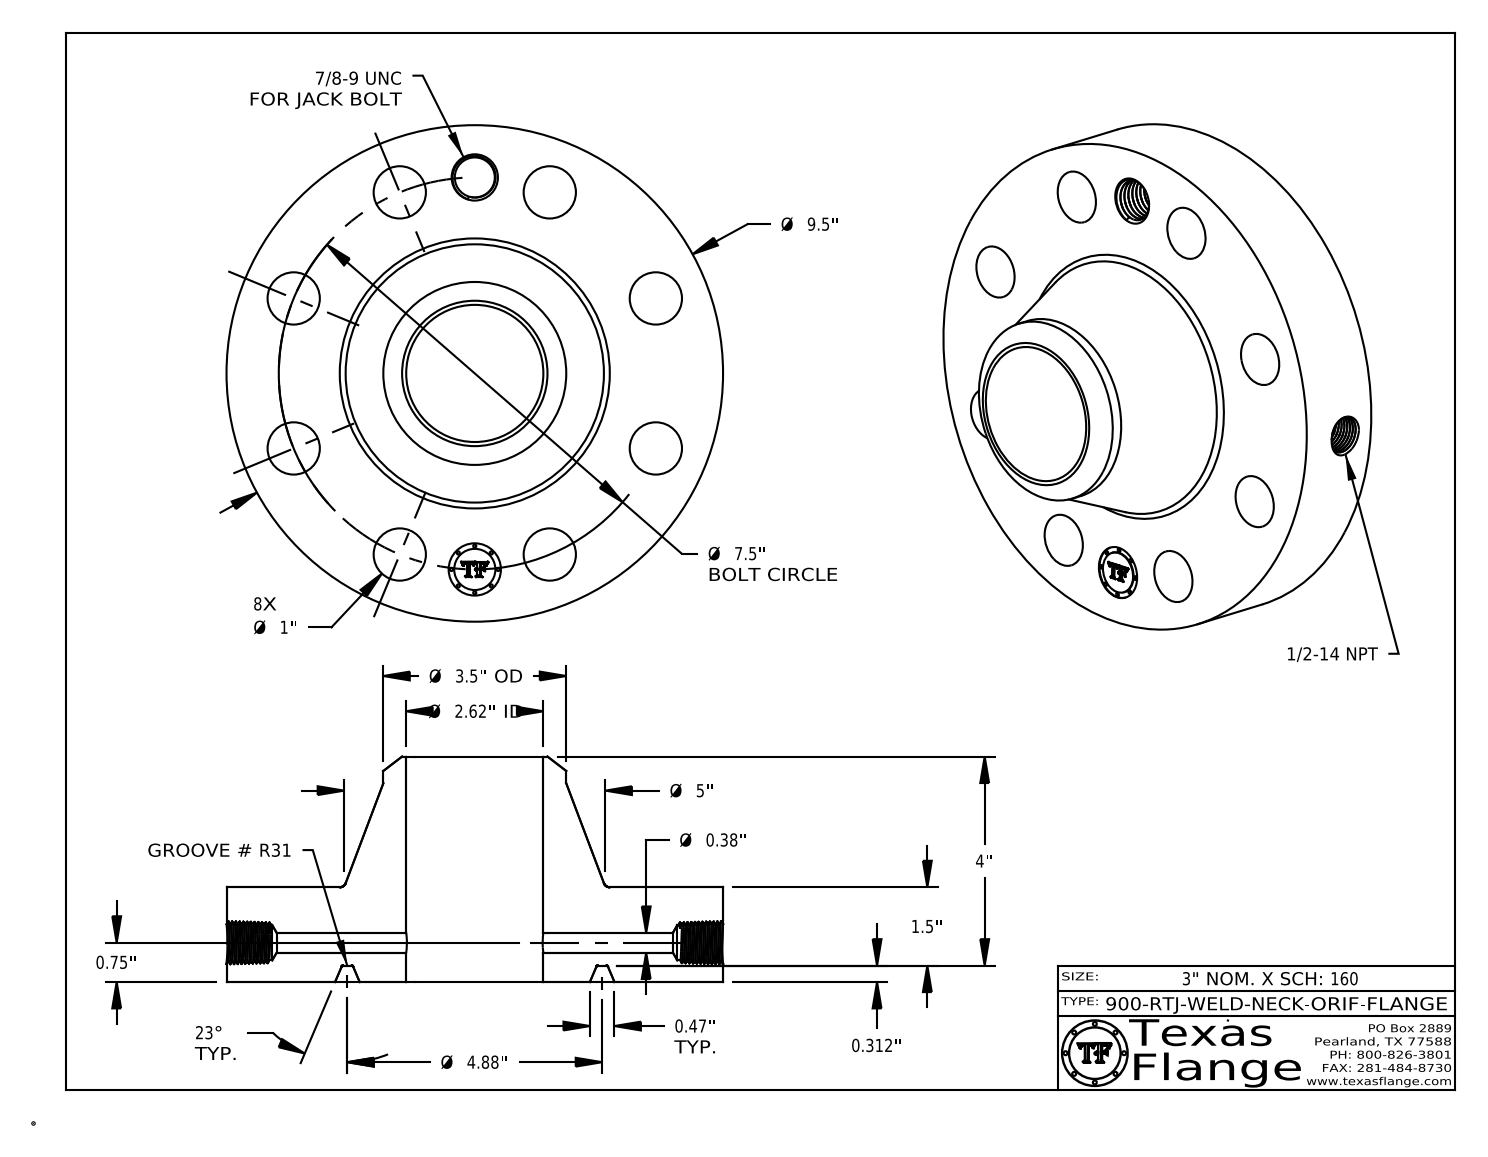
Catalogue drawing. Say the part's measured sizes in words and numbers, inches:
The part is named "900-RTJ-WELD-NECK". Its 3-D file was written by "CATIA V5 STEP AP214 (AUTOMOTIVE_DESIGN)". It is 1 solid with 784 faces: 370 planar, 94 cylindrical and 320 other. Overall it measures 9.5 by 9.5 by 4.312 inches. Its volume is 122.8 cubic inches and its surface area 299.3 square inches. Round holes: 9 of diameter 1, 1 of diameter 0.375, 1 of diameter 0.672, 1 of diameter 0.766, 1 of diameter 2.624. Round bosses or shafts: 8 of diameter 0.061, 1 of diameter 9.5, 1 of diameter 3.5, 1 of diameter 0.788. The main face-to-face distances are 1.812, 0.312, 1.5, 4.312, 4, 2.5, 1.797, 1.485, 0.015, 2.515. The hole center spacings are 3.75, 2.87, 5.303, 6.929, 7.5, 1.463, 4.167, 6.236.
